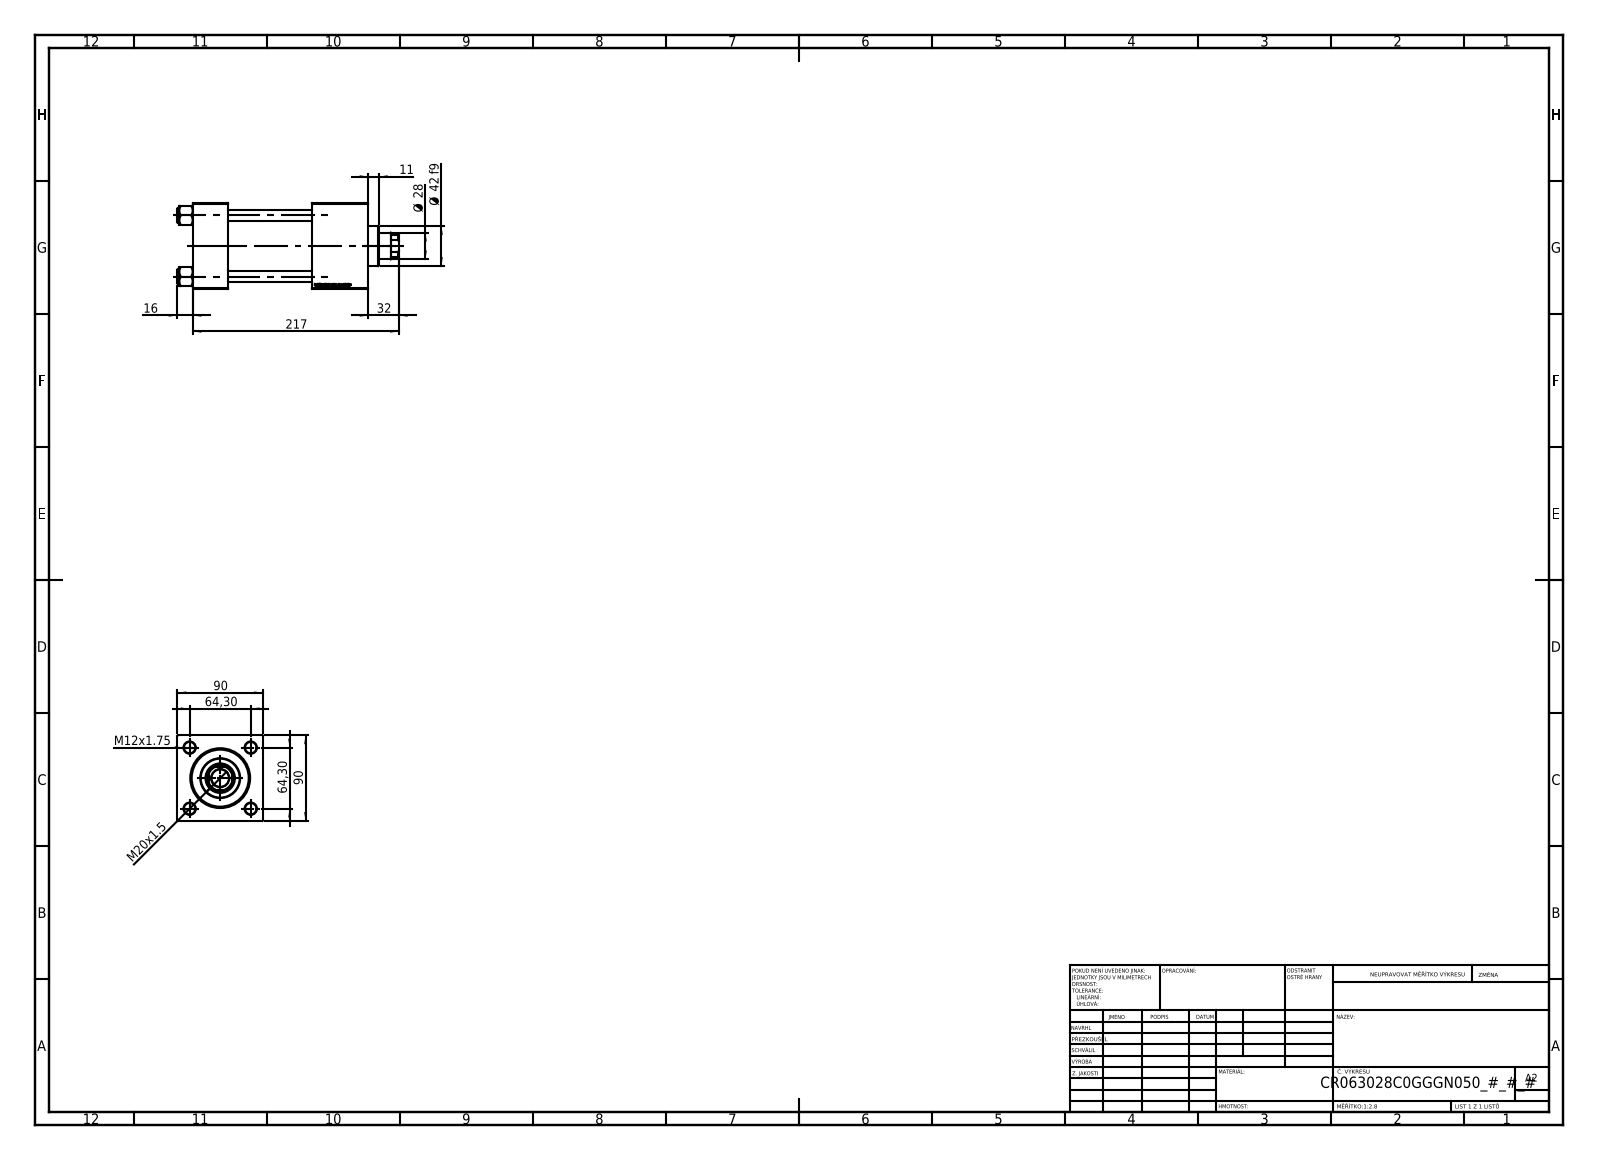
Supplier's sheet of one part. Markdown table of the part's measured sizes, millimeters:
| quantity | value |
| --- | --- |
| part name | V215CR_C_Body; NUT_M5_C; V215CR_VCP_C; V215_VC_A (+1 more) |
| STEP written by | SolidWorks 2019 (CONFIG_CONTROL_DESIGN) |
| units | millimeters |
| bodies | 11 solids, 1149 faces (526 planar, 87 cylindrical, 536 other) |
| overall size | 233 × 90 × 90 |
| volume | 997 468 mm³ |
| surface area | 198 737 mm² |
| round holes (diameter × count) | 12 × 4, 7 × 2, 20.96 × 2, 30 × 2, 18.5 × 1, 28 × 1, 31 × 1, 50 × 1, 60 × 1, 63 × 1 |
| round bosses / shafts (diameter × count) | 15 × 4, 69 × 1, 42 × 1 |
| partial cylindrical surfaces (radius × count) | 13.5 × 1 |
| main face-to-face distances | 90, 37, 185, 148, 126, 89, 59, 156.3, 119.3, 30.3 |
| hole center spacings | 45.47, 64.3, 90.93, 127.5 |
